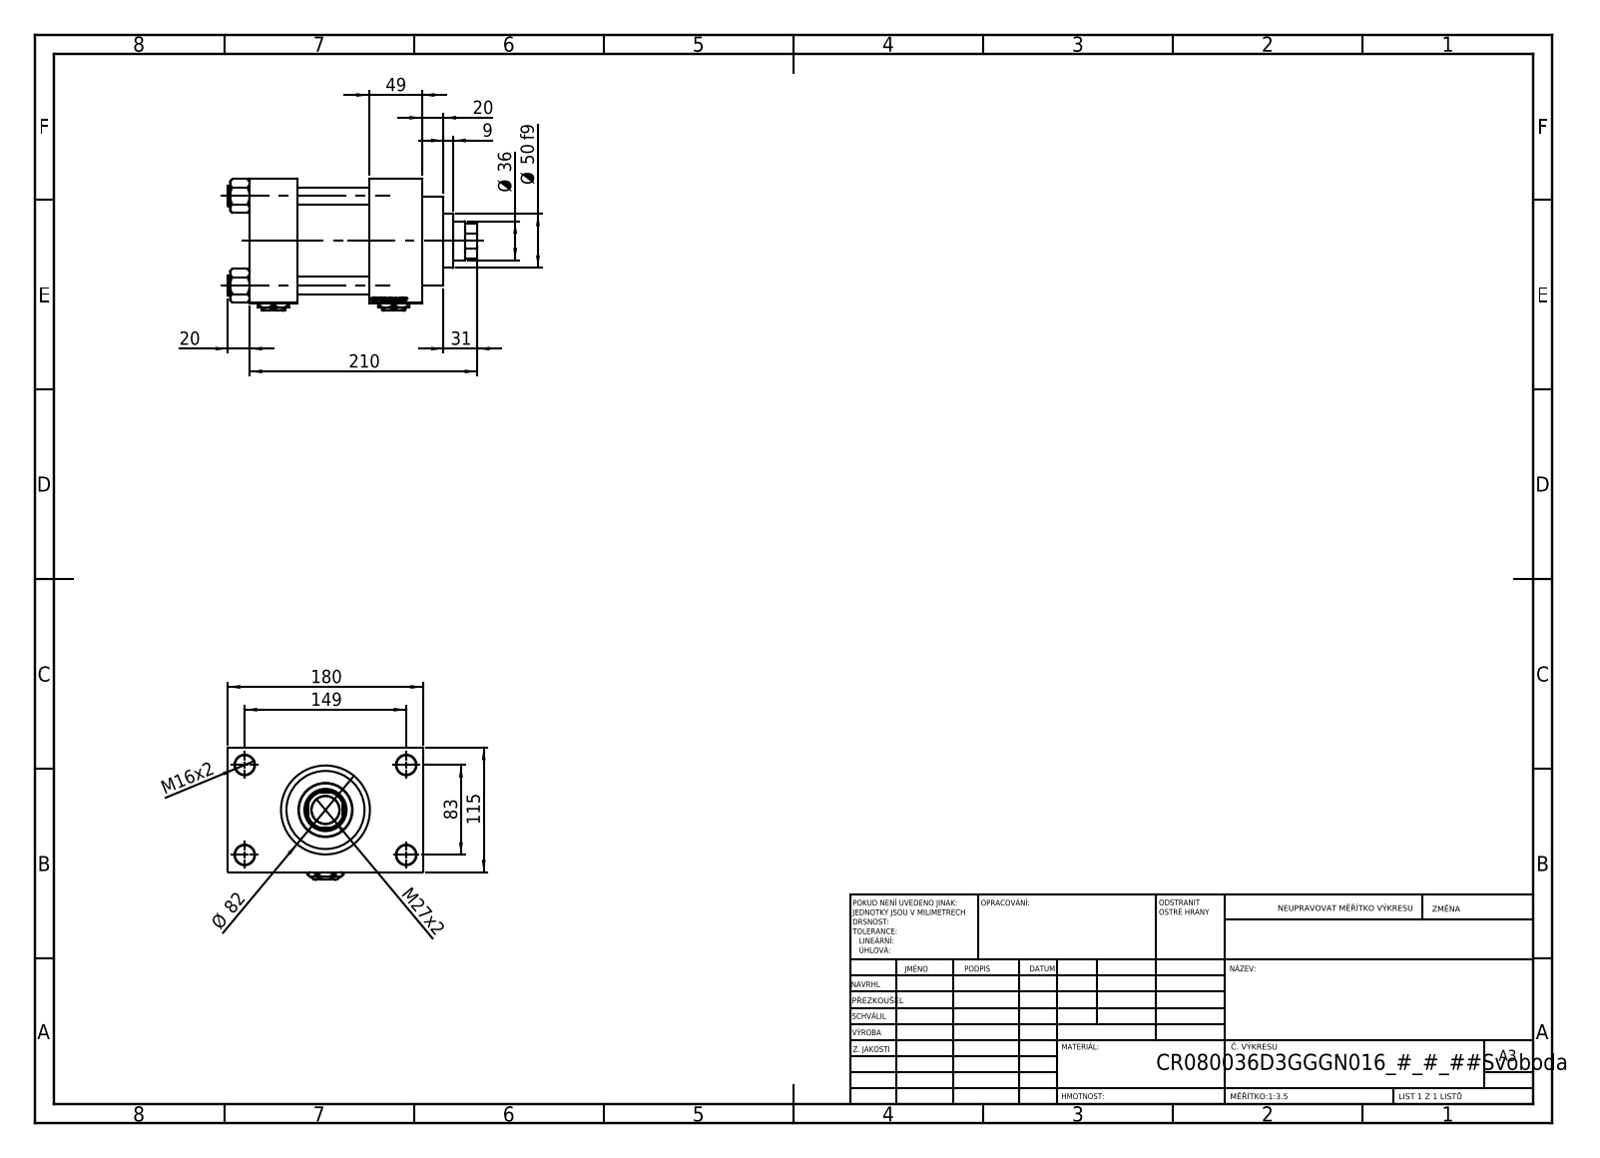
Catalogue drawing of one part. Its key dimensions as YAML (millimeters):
part_name: "V215CR_D_TYCINKA; V215CR_D_Body; Zatka_pro_OIL_PORT; V215CR_VCP_D (+2 more)"
step_written_by: "SolidWorks 2019 (CONFIG_CONTROL_DESIGN)"
units: millimeters
bodies: {solids: 13, faces: 1253, planar: 593, cylindrical: 100, other: 560}
overall_size: [230, 180, 122]
volume: 1983000
surface_area: 300614
round_holes:
  - {diameter: 16, count: 4}
  - {diameter: 18, count: 4}
  - {diameter: 7, count: 2}
  - {diameter: 26.44, count: 2}
  - {diameter: 35, count: 2}
  - {diameter: 25.5, count: 1}
  - {diameter: 36, count: 1}
  - {diameter: 39, count: 1}
  - {diameter: 61, count: 1}
  - {diameter: 72, count: 1}
  - {diameter: 80, count: 1}
round_bosses_or_shafts:
  - {diameter: 19, count: 4}
  - {diameter: 86, count: 1}
  - {diameter: 82, count: 1}
  - {diameter: 50, count: 1}
partial_cylinders:
  - {radius: 17.5, count: 1}
face_to_face_distances: [115, 66, 110, 49, 44, 159, 147.5, 32.5, 20, 69]
hole_center_spacings: [33.15, 58.48, 82.7, 85.28, 89.24, 115.85, 142.43, 83]
